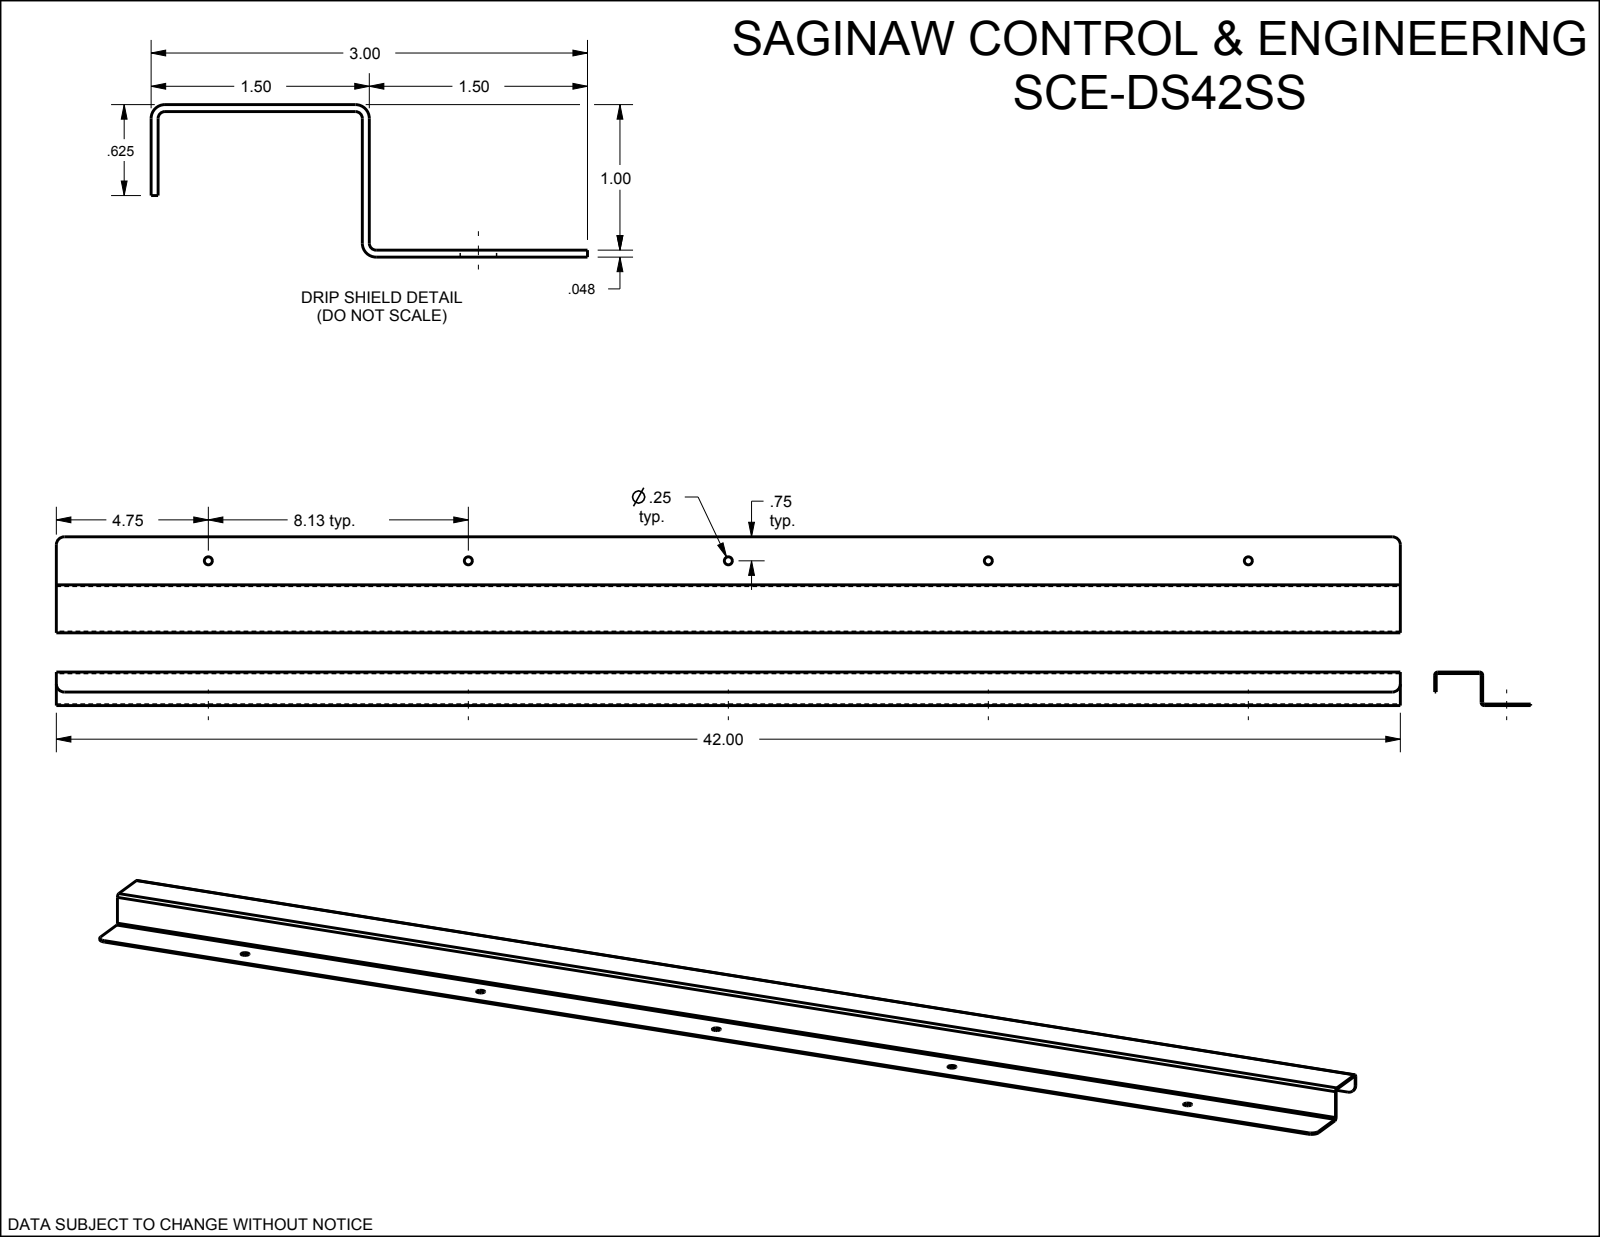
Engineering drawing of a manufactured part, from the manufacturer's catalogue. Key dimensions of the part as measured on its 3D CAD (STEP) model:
Part name (STEP PRODUCT): SCE-DS42SS
STEP written by: SolidWorks 2019 (CONFIG_CONTROL_DESIGN)
Units: inches
Bodies: 1 solid, 27 faces (12 planar, 15 cylindrical, 0 other)
Overall size (bounding box): 42 × 3 × 1.048
Volume: 9.029 in³ · Surface area: 380.8 in²
Round holes (diameter × count): ⌀0.25 ×5
Partial cylindrical surfaces — rounded edges, fillets, slot ends (radius × count): R0.25 ×4, R0.047 ×3, R0.095 ×3
Main face-to-face distances: 0.048, 1, 0.952, 1.048, 1.452, 1.5, 1.404, 0.423, 0.375, 0.577
Hole centre spacings: 8.125, 8.125, 16.25, 24.375, 16.25, 32.5
